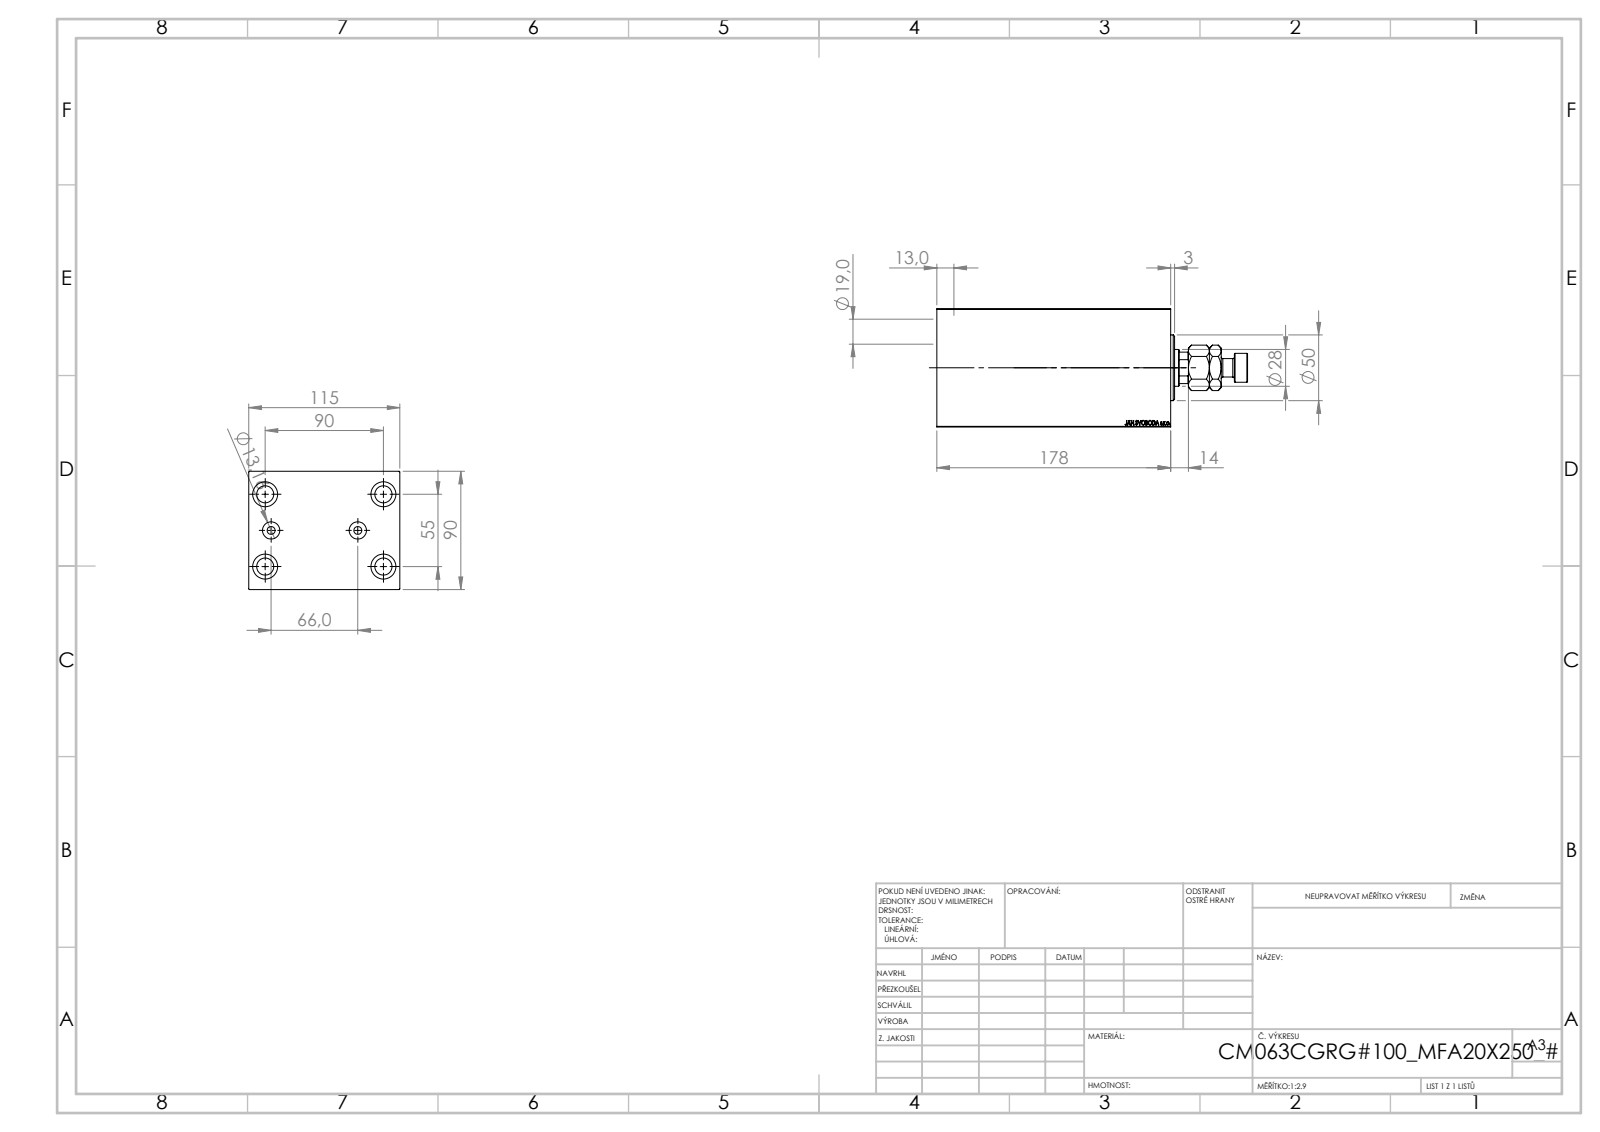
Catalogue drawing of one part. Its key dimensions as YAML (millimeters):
part_name: "MFA; V450CM_C_VCP; V450CM_C_Body; V450CM_VC_B"
step_written_by: "SolidWorks 2019 (CONFIG_CONTROL_DESIGN)"
units: millimeters
bodies: {solids: 4, faces: 913, planar: 425, cylindrical: 62, other: 426}
overall_size: [236.5, 115, 90]
volume: 1500000
surface_area: 192834
round_holes:
  - {diameter: 13, count: 4}
  - {diameter: 19, count: 4}
  - {diameter: 6, count: 2}
  - {diameter: 13.16, count: 2}
  - {diameter: 18.5, count: 1}
  - {diameter: 28, count: 1}
  - {diameter: 31.5, count: 1}
  - {diameter: 63, count: 1}
  - {diameter: 65, count: 1}
  - {diameter: 72, count: 1}
round_bosses_or_shafts:
  - {diameter: 50, count: 1}
  - {diameter: 22, count: 1}
  - {diameter: 14, count: 1}
partial_cylinders:
  - {radius: 13.5, count: 1}
face_to_face_distances: [90, 115, 178, 46, 132, 168, 10, 5, 122, 68]
hole_center_spacings: [30, 52.74, 82.71, 33, 55, 90, 105.48, 66]
